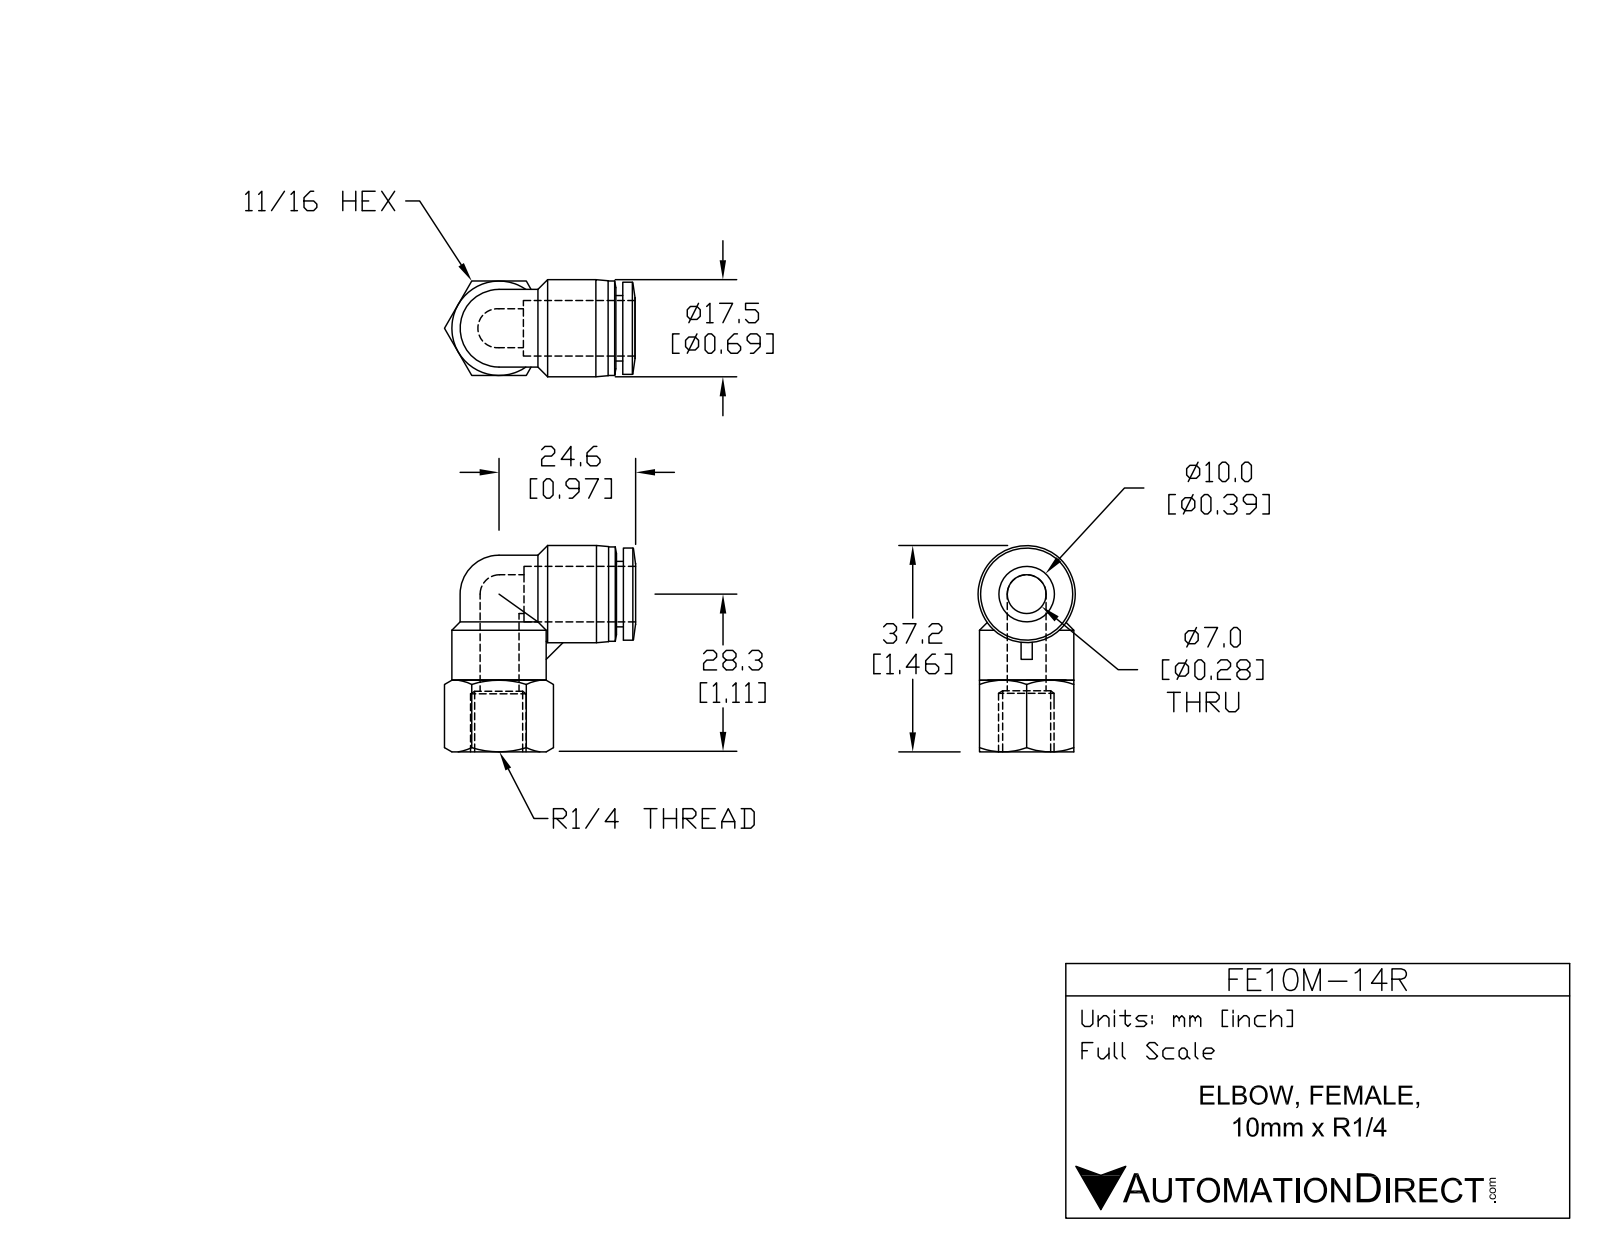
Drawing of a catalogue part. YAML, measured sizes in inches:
part_name: "FE10M-14R"
step_written_by: "SolidWorks 2015 (AUTOMOTIVE_DESIGN)"
units: inches
bodies: {solids: 1, faces: 69, planar: 16, cylindrical: 20, other: 33}
overall_size: [1.467, 1.355, 0.689]
volume: 0.443
surface_area: 7.603
round_holes:
  - {diameter: 0.276, count: 2}
  - {diameter: 0.406, count: 1}
round_bosses_or_shafts:
  - {diameter: 0.669, count: 2}
  - {diameter: 0.689, count: 1}
  - {diameter: 0.654, count: 1}
  - {diameter: 0.551, count: 1}
  - {diameter: 0.465, count: 1}
partial_cylinders:
  - {radius: 0.276, count: 1}
face_to_face_distances: [0.669, 0.433, 0.049, 0.659, 0.709, 0.295, 0.374, 0.079, 0.604, 0.055]
